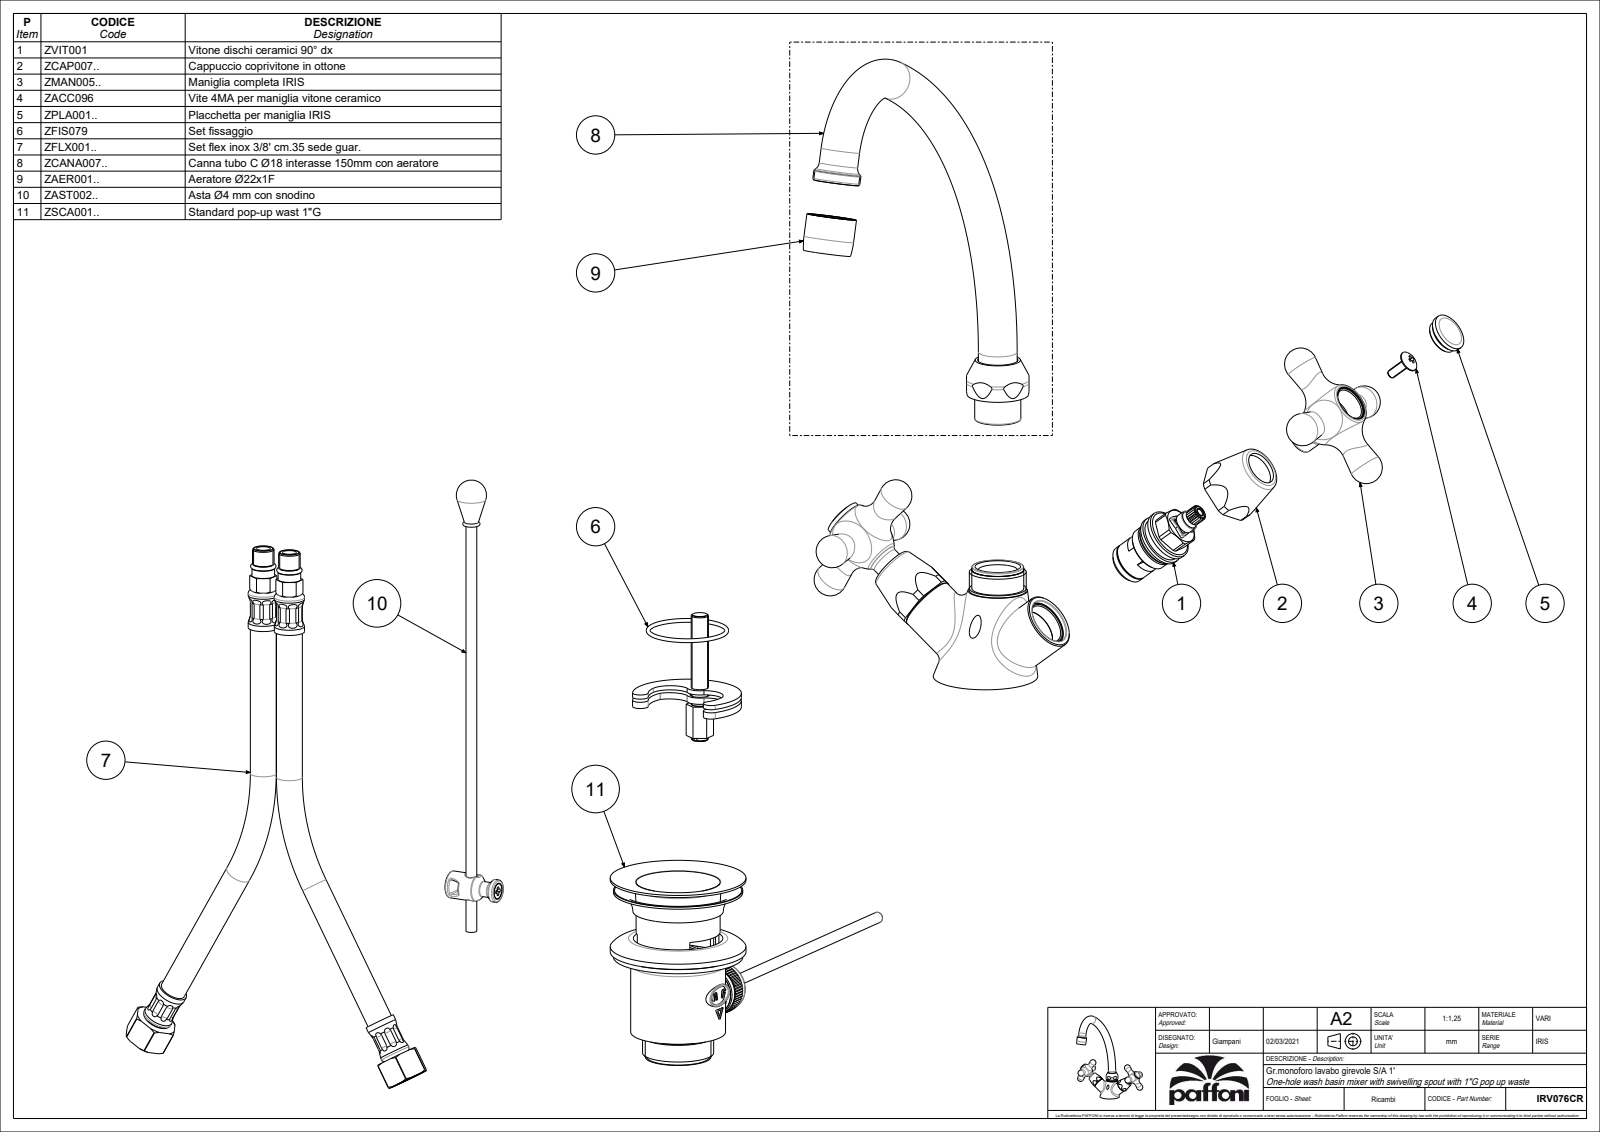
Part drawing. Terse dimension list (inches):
name: IRV076CR
written by: CREO PARAMETRIC BY PTC INC, 2020044 (CONFIG_CONTROL_DESIGN)
unit: in
bodies: 2 solids, 484 faces (139 planar, 106 cylindrical, 239 other)
size: 8.996 × 7.513 × 7.243
volume: 11.64 in³; area: 92.68 in²
holes: 4× ⌀0.354, 2× ⌀0.315, 2× ⌀0.433, 2× ⌀0.618, 2× ⌀0.709, 2× ⌀0.748, 2× ⌀0.827, 2× ⌀0.846, 2× ⌀0.906, 1× ⌀0.217, 1× ⌀0.236, 1× ⌀0.268
bosses: 4× ⌀0.709, 2× ⌀1.035, 2× ⌀0.531, 1× ⌀1.339, 1× ⌀1.039, 1× ⌀0.913, 1× ⌀0.866, 1× ⌀0.705
rounds: 2× R0.571
face distances: 1.043, 0.866, 0.945, 1.681, 0.051, 1.63, 1.811, 0.079, 1.043, 0.941
hole spacings: 0.276, 0.465, 0.527, 0.547, 0.024, 0.374, 0.449, 0.472
